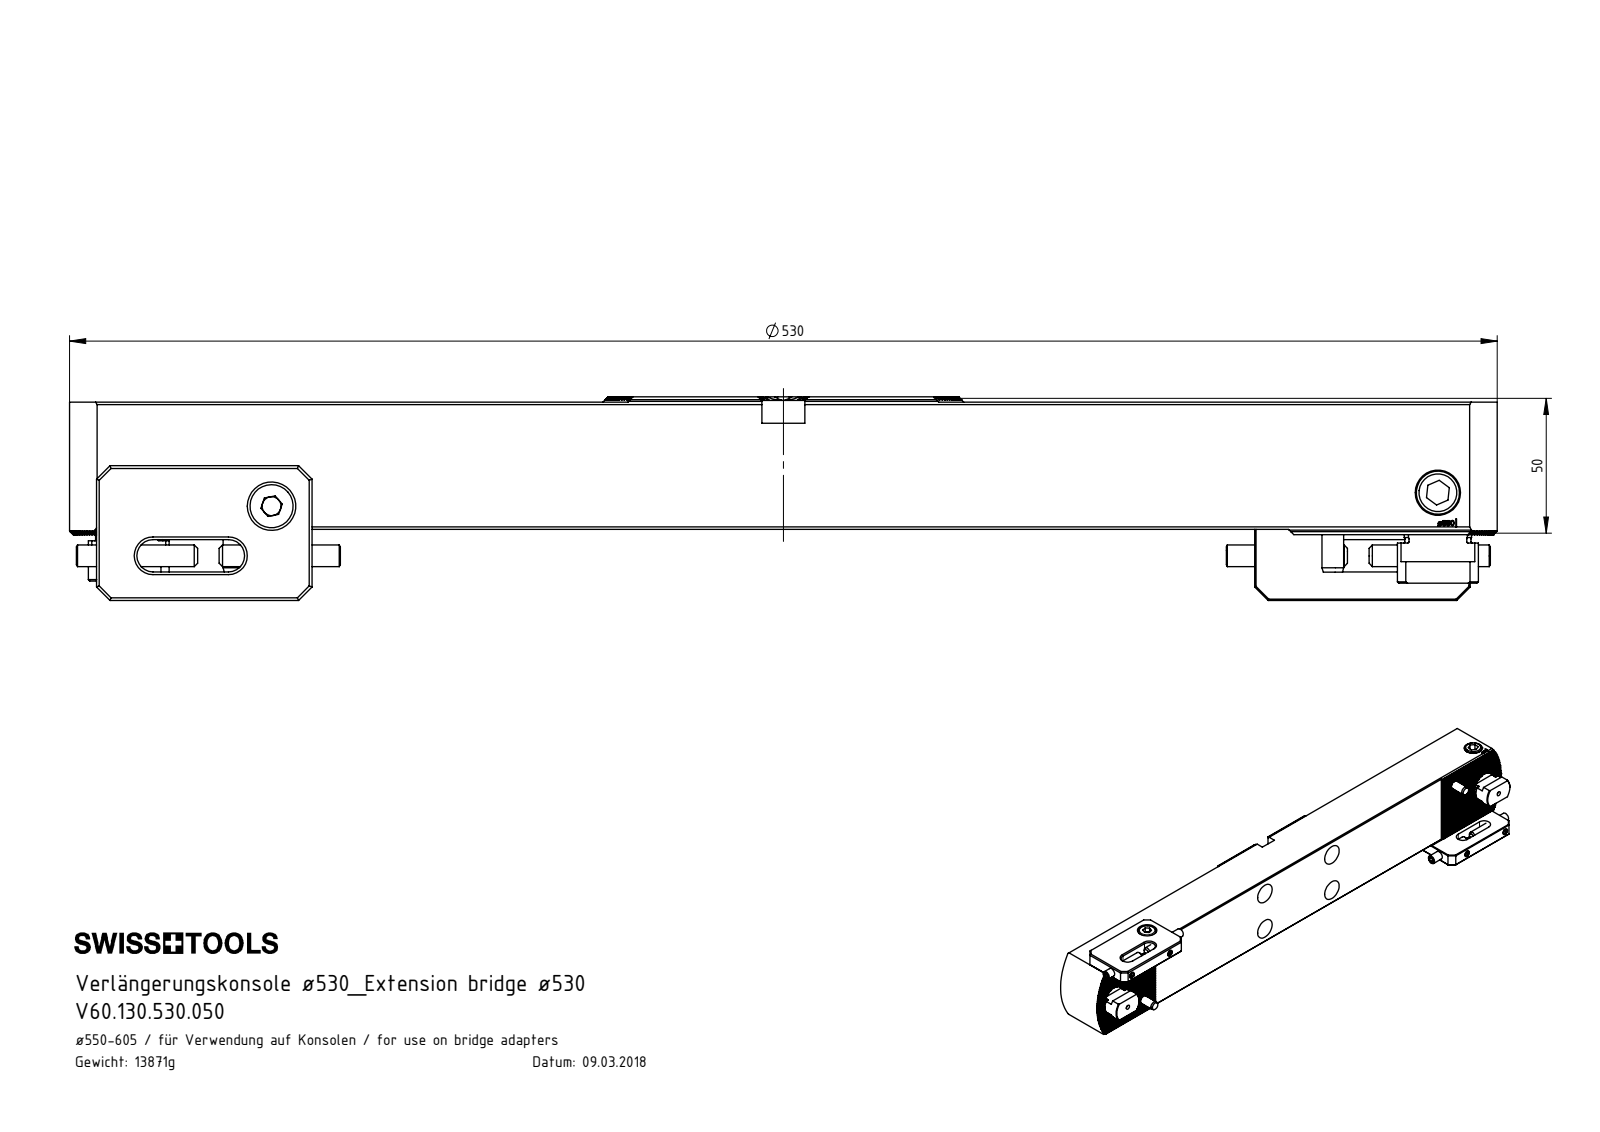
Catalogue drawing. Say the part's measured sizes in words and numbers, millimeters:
The part is named "Ko1.VK1.530.050; VK1-ER3.001.028_A; VK1-ER7.001.012_B; VK1-ER2.101.010_A (+8 more)". Its 3-D file was written by "SolidWorks 2017 (AUTOMOTIVE_DESIGN)". It is 27 solids with 1331 faces: 874 planar, 260 cylindrical and 197 other. Overall it measures 530 by 94 by 75.58 millimeters. Its volume is 1 773 000 cubic millimeters and its surface area 214 240 square millimeters. Round holes: 4 of diameter 5, 4 of diameter 6, 4 of diameter 6.8, 4 of diameter 13, 4 of diameter 19, 2 of diameter 2, 2 of diameter 8, 2 of diameter 8.5, 2 of diameter 10.5, 2 of diameter 11, 2 of diameter 14, 2 of diameter 18. Round bosses or shafts: 4 of diameter 16, 4 of diameter 6, 2 of diameter 10, 2 of diameter 8. Partial cylindrical surfaces (rounded edges, fillets, slot ends): 66 of radius 0.14, 8 of radius 2, 4 of radius 6, 2 of radius 12.3, 2 of radius 15, 2 of radius 65, 1 of radius 7.95. The main face-to-face distances are 47.16, 70, 12, 82, 1.73, 8.66, 3.46, 6.93, 0.5, 41.57. The hole center spacings are 486, 200, 287.7, 7.9, 18.55, 19.61, 34.53, 35.09.
